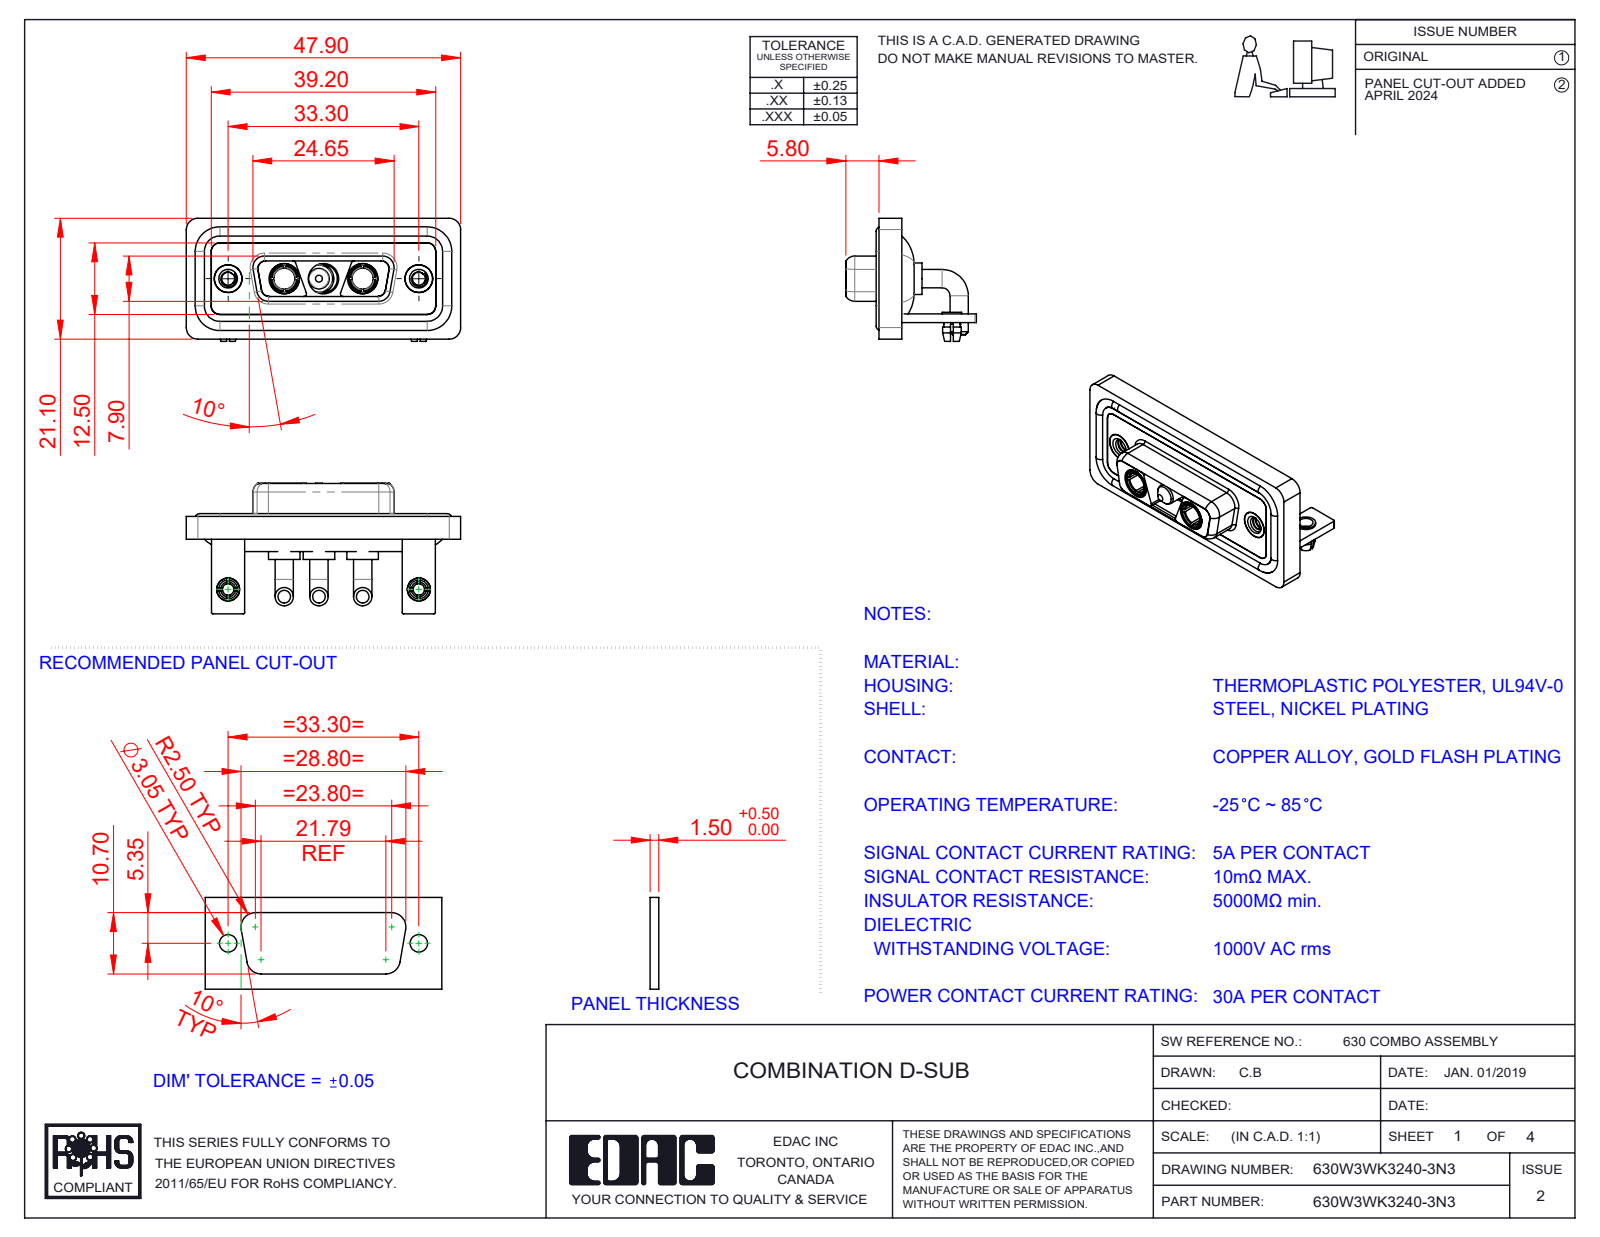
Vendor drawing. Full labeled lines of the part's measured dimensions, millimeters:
Part name (STEP PRODUCT): Power Socket_30A RA; 630Combo Housing_3WK3; 630Combo Stabilizer Bracket_50 Contacts; 630Combo Board Lock_50 Contacts (+6 more)
STEP written by: SolidWorks 2023 (CONFIG_CONTROL_DESIGN)
Units: millimetres
Bodies: 17 solids, 735 faces (246 planar, 320 cylindrical, 169 other)
Overall size (bounding box): 47.9 × 22.8 × 21.5
Volume: 6 519 mm³ · Surface area: 10 739 mm²
Round holes (diameter × count): ⌀4.85 ×5, ⌀5.3 ×3, ⌀2 ×2, ⌀2.26 ×2, ⌀2.5 ×2, ⌀3.2 ×2, ⌀3.7 ×2, ⌀4 ×2, ⌀4.05 ×2, ⌀5 ×2
Round bosses / shafts (diameter × count): ⌀3.2 ×6, ⌀1.6 ×4, ⌀5.5 ×3, ⌀5.2 ×3, ⌀4.75 ×3, ⌀3.75 ×3, ⌀4.96 ×2, ⌀4.95 ×2
Partial cylindrical surfaces — rounded edges, fillets, slot ends (radius × count): R2 ×21, R1.5 ×18, R0.25 ×16, R1.35 ×12, R0.5 ×9, R1.6 ×8, R0.6 ×4, R0.65 ×4
Main face-to-face distances: 0.4, 2.9, 1.5, 3.7, 1.8, 1.1, 4.1, 1.6, 2.5, 1.4
Hole centre spacings: 6.85, 9.8, 16.65, 23.5, 33.3, 13.7
